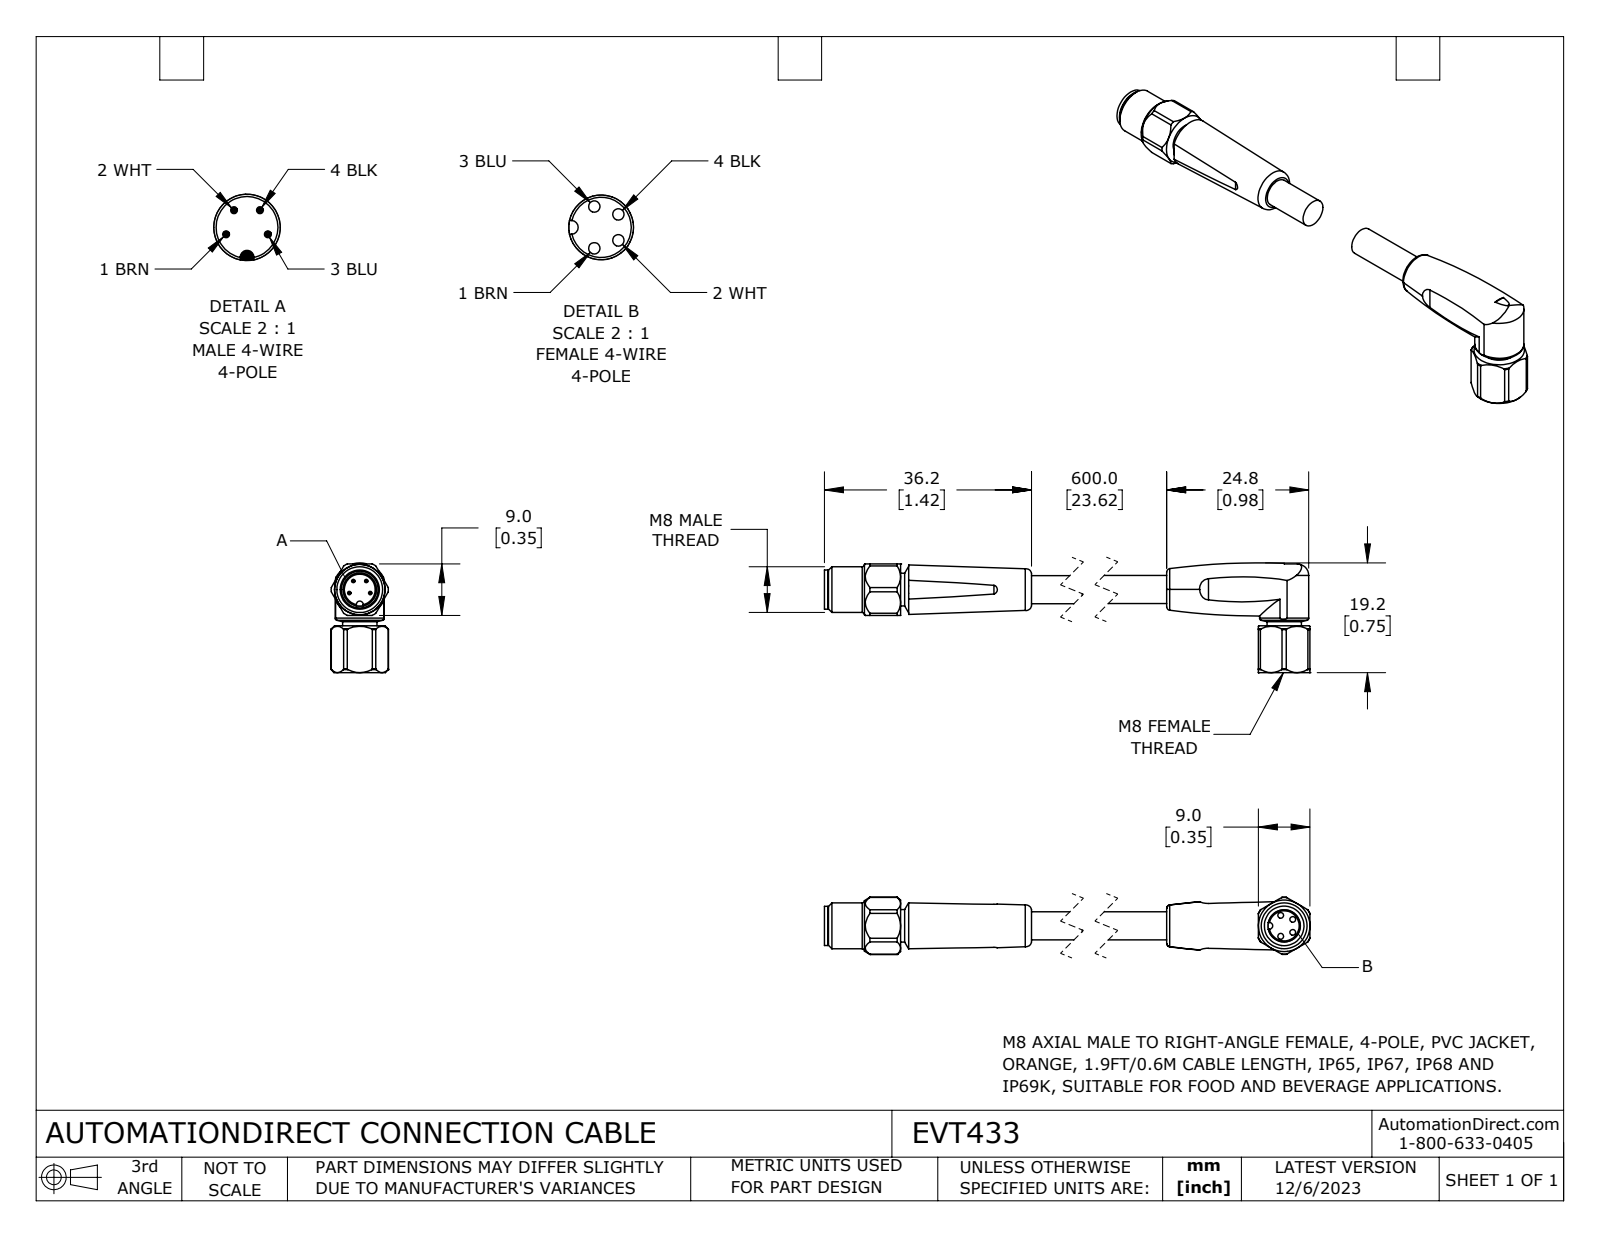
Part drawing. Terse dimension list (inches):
name: EVT433_MALE; EVT433_FEMALE; EVT433
written by: SolidWorks 2023 (CONFIG_CONTROL_DESIGN)
unit: in
bodies: 2 solids, 172 faces (52 planar, 59 cylindrical, 61 other)
size: 3.76 × 0.755 × 0.394
volume: 0.254 in³; area: 4.6 in²
holes: 4× ⌀0.039, 1× ⌀0.228, 1× ⌀0.272
bosses: 4× ⌀0.023, 2× ⌀0.193, 1× ⌀0.339, 1× ⌀0.315, 1× ⌀0.27, 1× ⌀0.248, 1× ⌀0.236, 1× ⌀0.224
rounds: 2× R0.024, 2× R0.126, 2× R0.133, 1× R0.196, 1× R0.197
face distances: 0.354, 0.354, 3.236, 2.882, 0.323, 0.748, 0.425, 0.394, 0.071, 0.327
hole spacings: 0.074, 0.076, 0.087, 0.143, 0.089, 0.143
